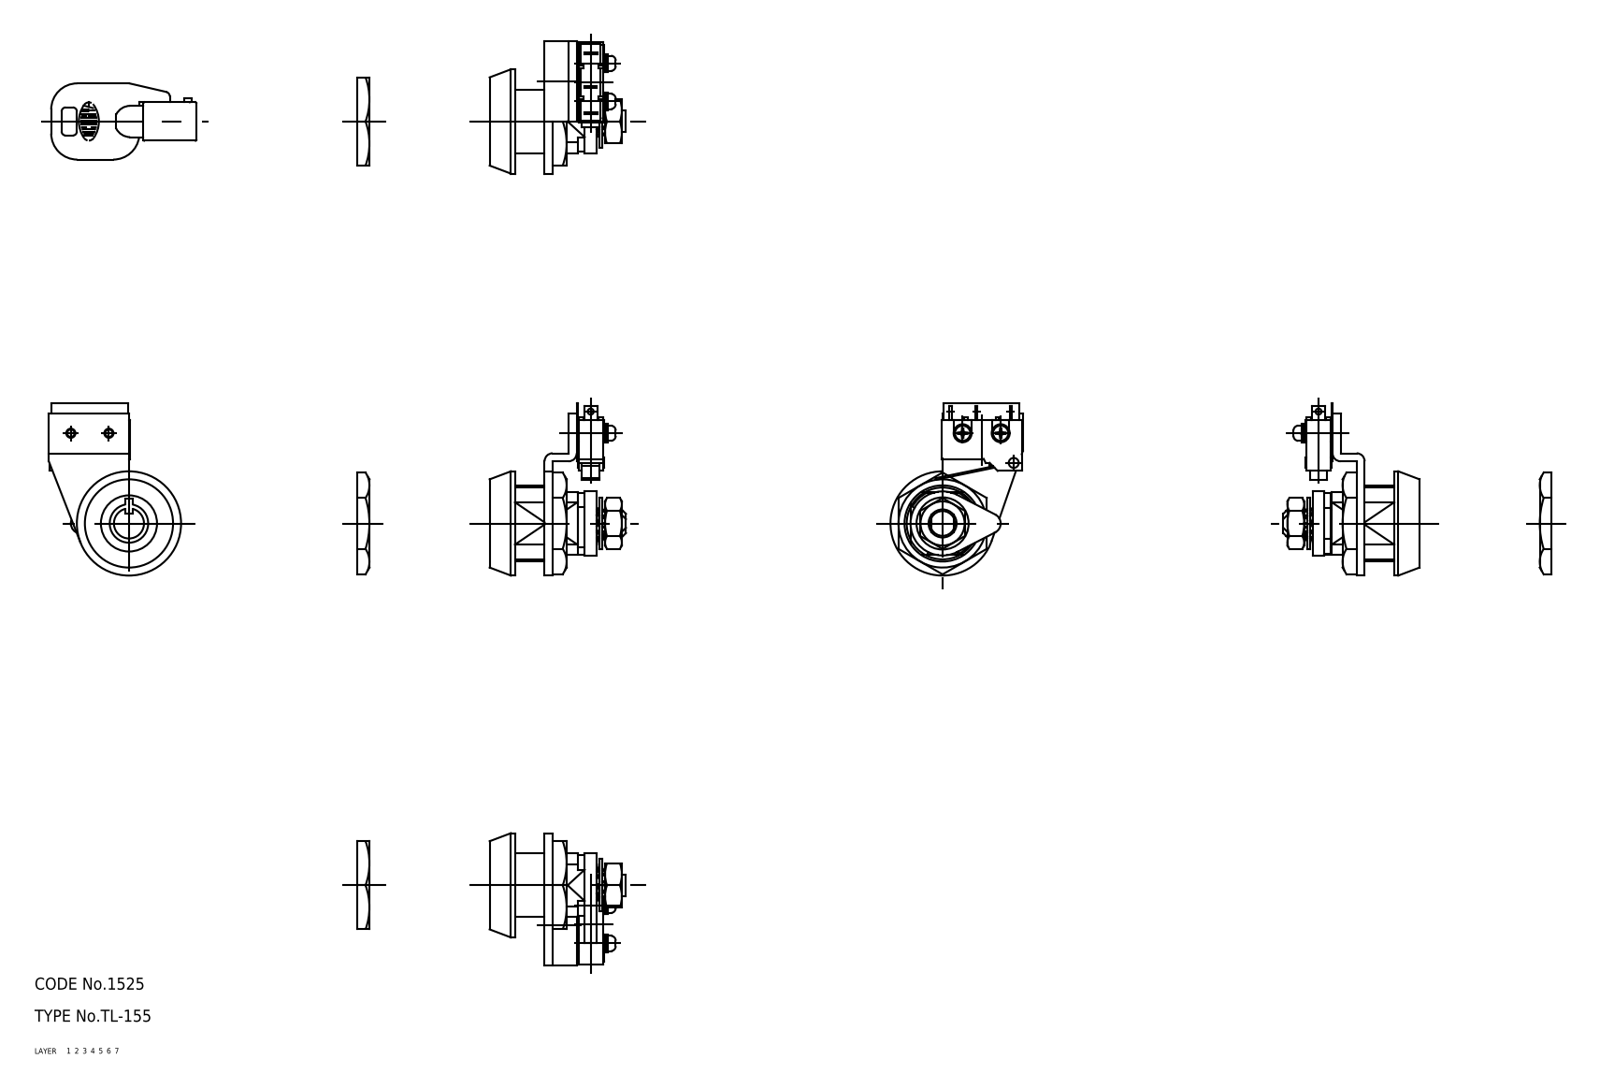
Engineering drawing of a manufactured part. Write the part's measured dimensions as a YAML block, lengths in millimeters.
part_name: "nut_A; screw; washer; switch_cam (+8 more)"
step_written_by: "CADfix (AUTOMOTIVE_DESIGN)"
units: millimeters
bodies: {solids: 14, faces: 389, planar: 0, cylindrical: 0, other: 389}
overall_size: [96.28, 43, 33]
volume: 13191
surface_area: 13183
